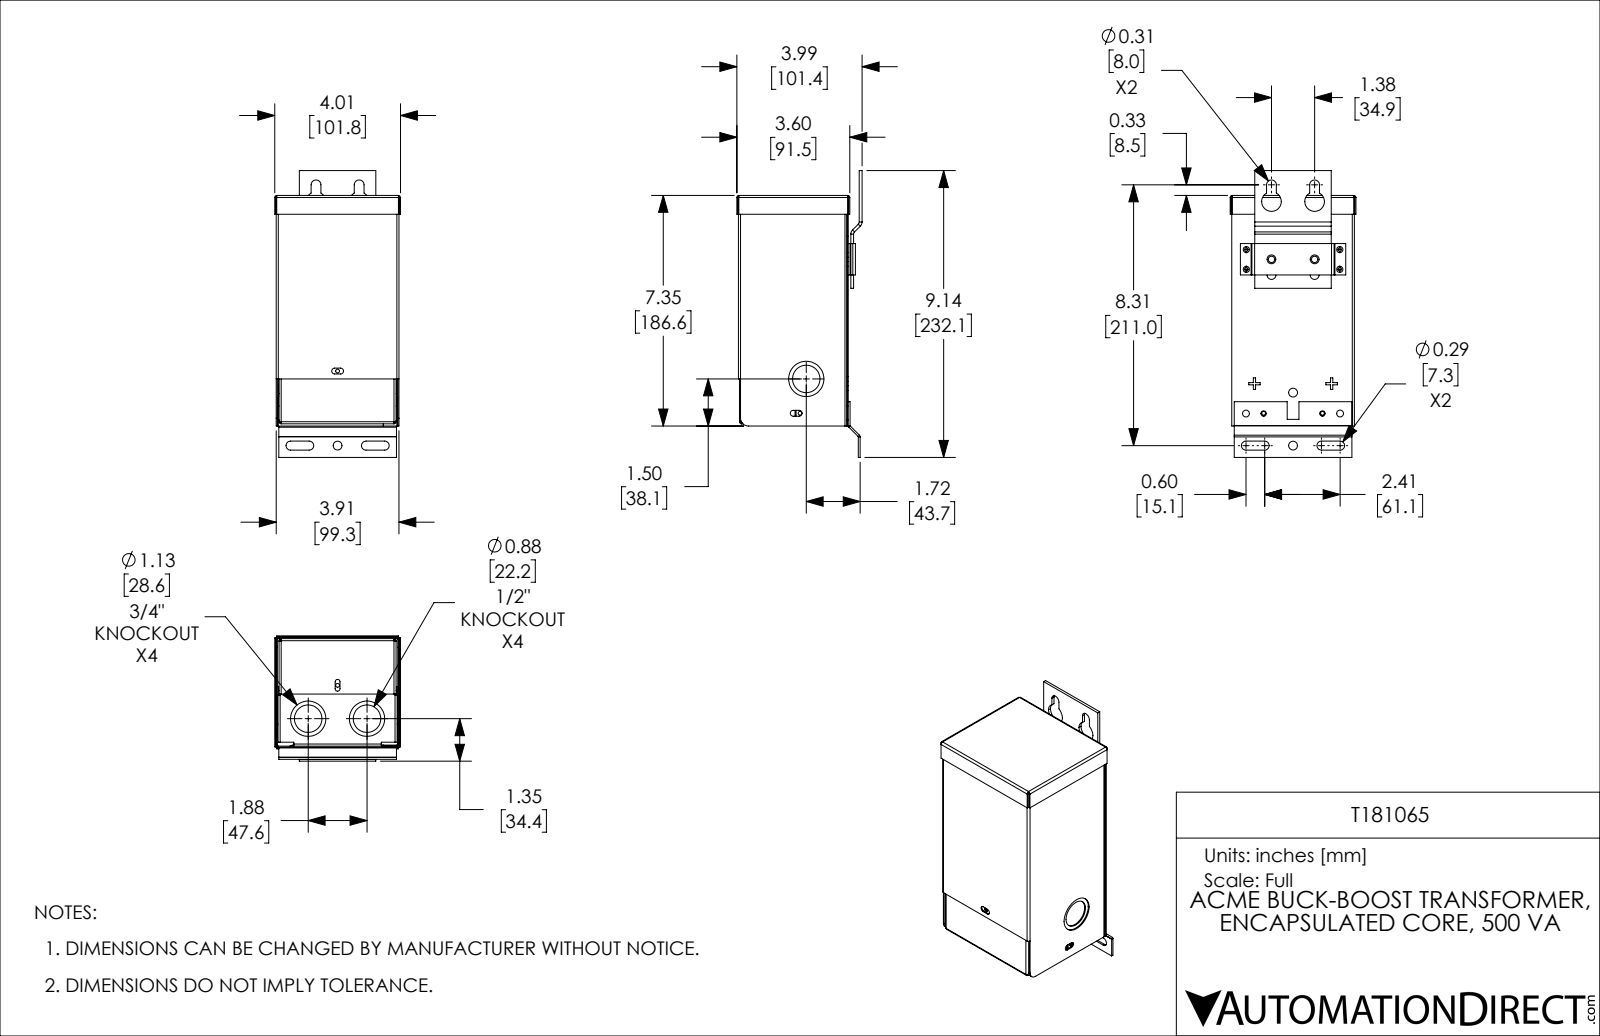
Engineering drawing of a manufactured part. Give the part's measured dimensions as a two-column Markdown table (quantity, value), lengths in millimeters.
| quantity | value |
| --- | --- |
| part name | T181065 |
| STEP written by | SolidWorks 2021 (CONFIG_CONTROL_DESIGN) |
| units | millimeters |
| bodies | 7 solids, 528 faces (326 planar, 154 cylindrical, 48 other) |
| overall size | 232.07 × 101.8 × 101.43 |
| volume | 113 073 mm³ |
| surface area | 227 401 mm² |
| round holes (diameter × count) | 3.05 × 5, 7.14 × 3, 7.14 × 3, 22.22 × 3, 28.57 × 3, 4.34 × 2, 4.76 × 2, 5.11 × 2, 5.54 × 2, 15.88 × 2, 28.58 × 1 |
| round bosses / shafts (diameter × count) | 30.4 × 3, 24.05 × 3 |
| partial cylindrical surfaces (radius × count) | 0.79 × 16, 1.7 × 16, 2.38 × 8, 0.66 × 4, 2.18 × 4, 3.66 × 4, 0.43 × 2, 1.96 × 2 |
| main face-to-face distances | 0.91, 87.99, 98.41, 87.08, 99.32, 97.5, 88.9, 1.53, 183.95, 182.42 |
| hole center spacings | 34.92, 12.7, 12.74, 14.27, 14.29, 29.09, 29.23, 34.94 |
